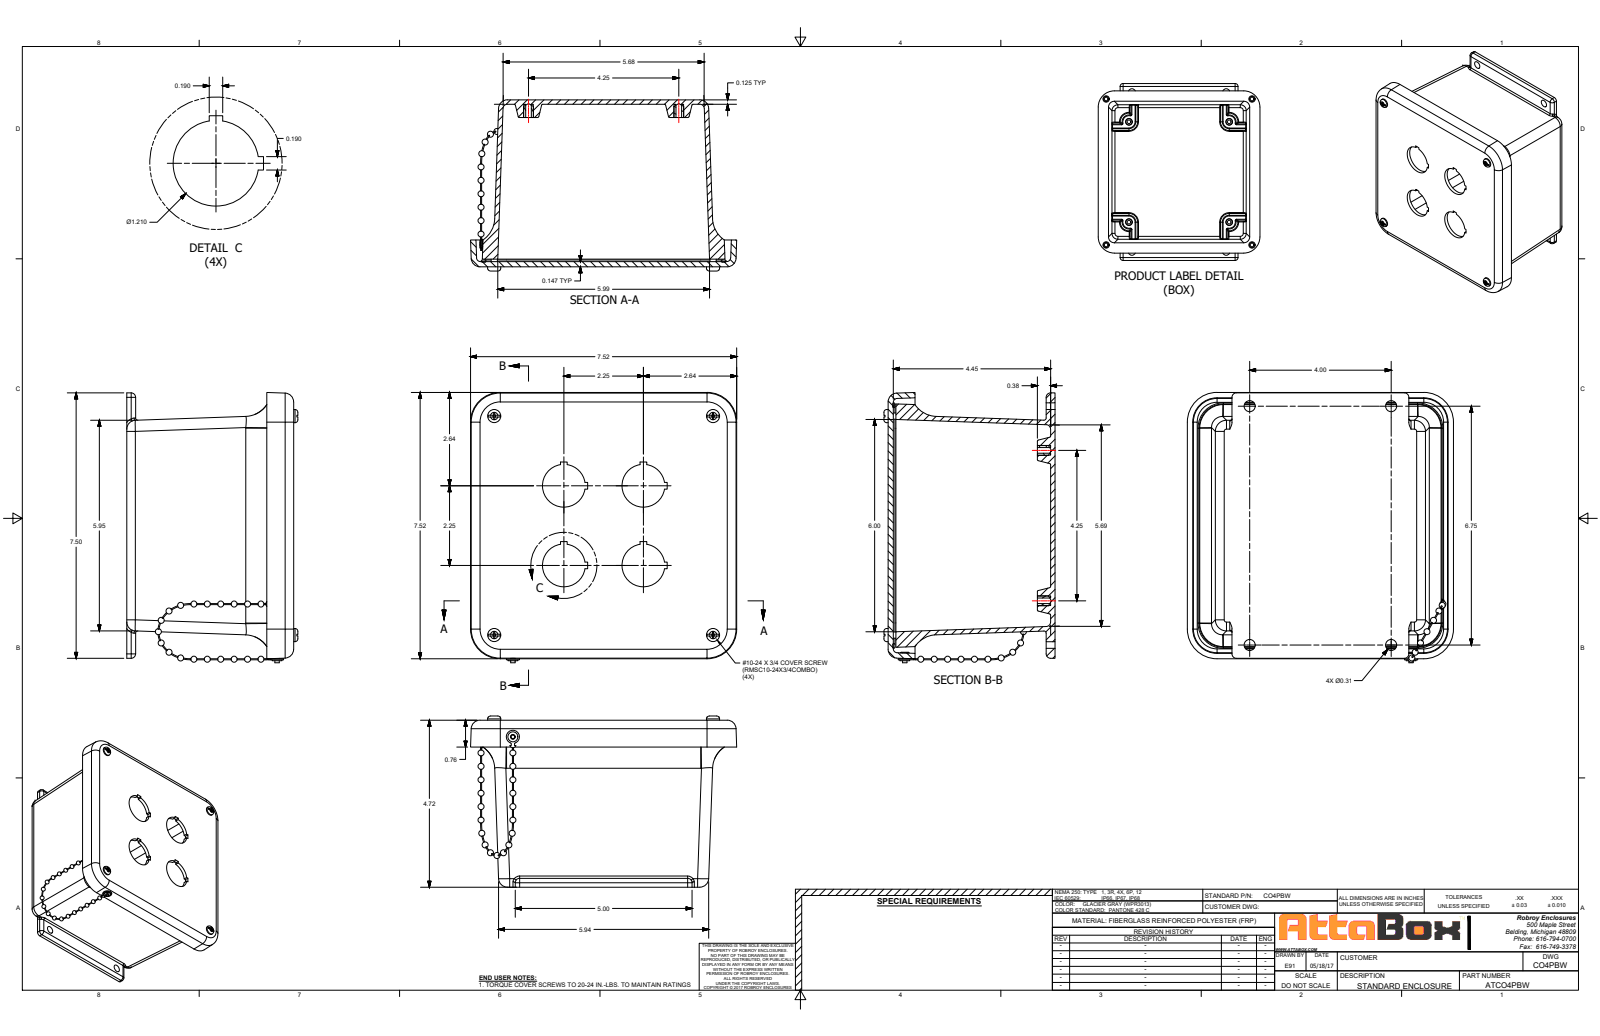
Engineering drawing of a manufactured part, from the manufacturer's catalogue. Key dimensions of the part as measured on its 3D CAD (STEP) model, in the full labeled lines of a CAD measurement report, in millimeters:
Part name (STEP PRODUCT): CO4PBW
STEP written by: SolidWorks 2018 (AUTOMOTIVE_DESIGN)
Units: millimetres
Bodies: 40 solids, 619 faces (213 planar, 207 cylindrical, 199 other)
Overall size (bounding box): 194 × 191.1 × 122.9
Volume: 583 400 mm³ · Surface area: 300 600 mm²
Round holes (diameter × count): ⌀4 ×8, ⌀5.6 ×4, ⌀6.4 ×4, ⌀7.1 ×4, ⌀8 ×4, ⌀30.7 ×4, ⌀2.6 ×2, ⌀3.2 ×2, ⌀3.6 ×2
Round bosses / shafts (diameter × count): ⌀6.9 ×8, ⌀9.4 ×4, ⌀4.5 ×4, ⌀7.2 ×2, ⌀0.7 ×2, ⌀9.4 ×1, ⌀3.2 ×1, ⌀3.2 ×1
Partial cylindrical surfaces — rounded edges, fillets, slot ends (radius × count): R0.8 ×44, R0.3 ×16, R3.2 ×12, R6.4 ×12, R2.8 ×4, R8 ×4, R19.1 ×4, R0.8 ×2
Main face-to-face distances: 3.2, 3.7, 116.1, 119.9, 3.2, 113, 116.7, 3.9, 5.6, 114.3
Hole centre spacings: 134.8, 28.7, 31.9, 34.8, 57.2, 86.4, 86.4, 108
